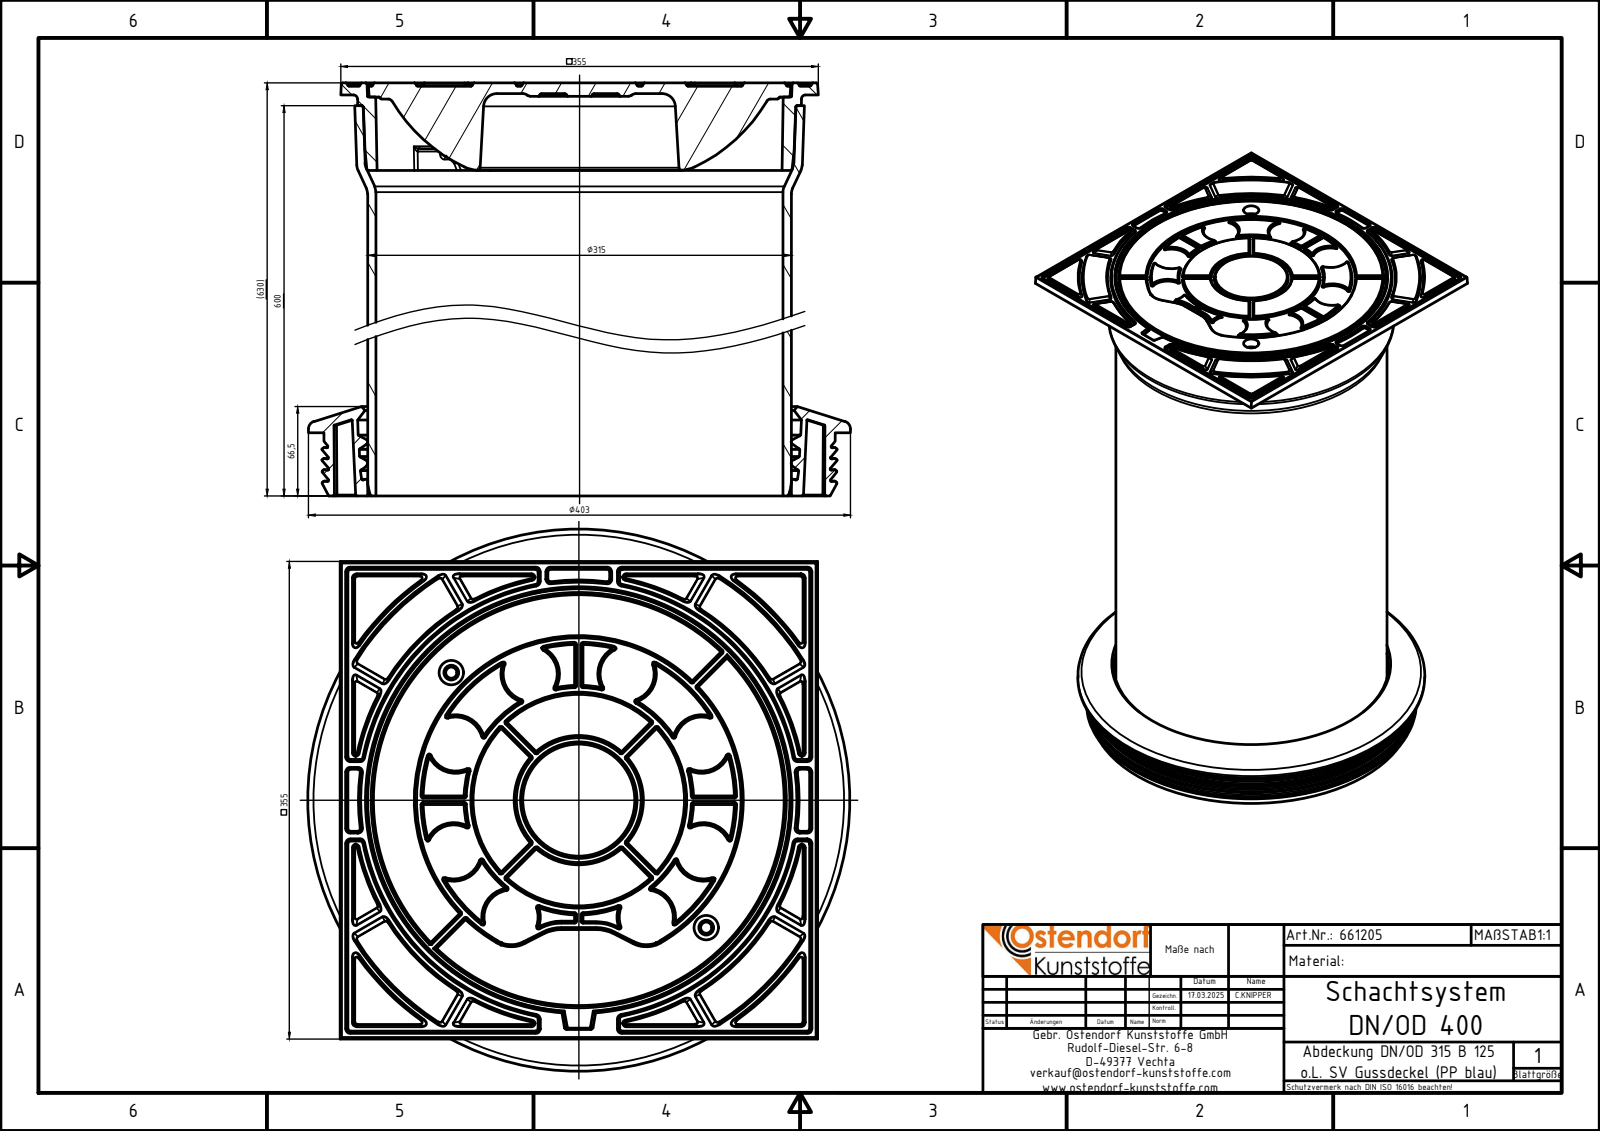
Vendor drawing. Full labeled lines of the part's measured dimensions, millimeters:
Part name (STEP PRODUCT): 661205z; 660205_Dichtungz; 990010_1z; 990010_2z (+1 more)
STEP written by: Autodesk Inventor 2024 (AUTOMOTIVE_DESIGN)
Units: millimetres
Bodies: 4 solids, 1524 faces (201 planar, 249 cylindrical, 1074 other)
Overall size (bounding box): 617 × 403 × 403
Volume: 8 129 000 mm³ · Surface area: 2 042 000 mm²
Round holes (diameter × count): ⌀8.38 ×2, ⌀11 ×2, ⌀18 ×2, ⌀302.6 ×1, ⌀315 ×1
Round bosses / shafts (diameter × count): ⌀403 ×1, ⌀380 ×1, ⌀330 ×1
Partial cylindrical surfaces — rounded edges, fillets, slot ends (radius × count): R1 ×160, R2 ×8, R2.5 ×8
Main face-to-face distances: 9, 2.5, 6.5, 8, 608, 614.5, 617, 1.5, 47, 561
Hole centre spacings: 134, 267.99
